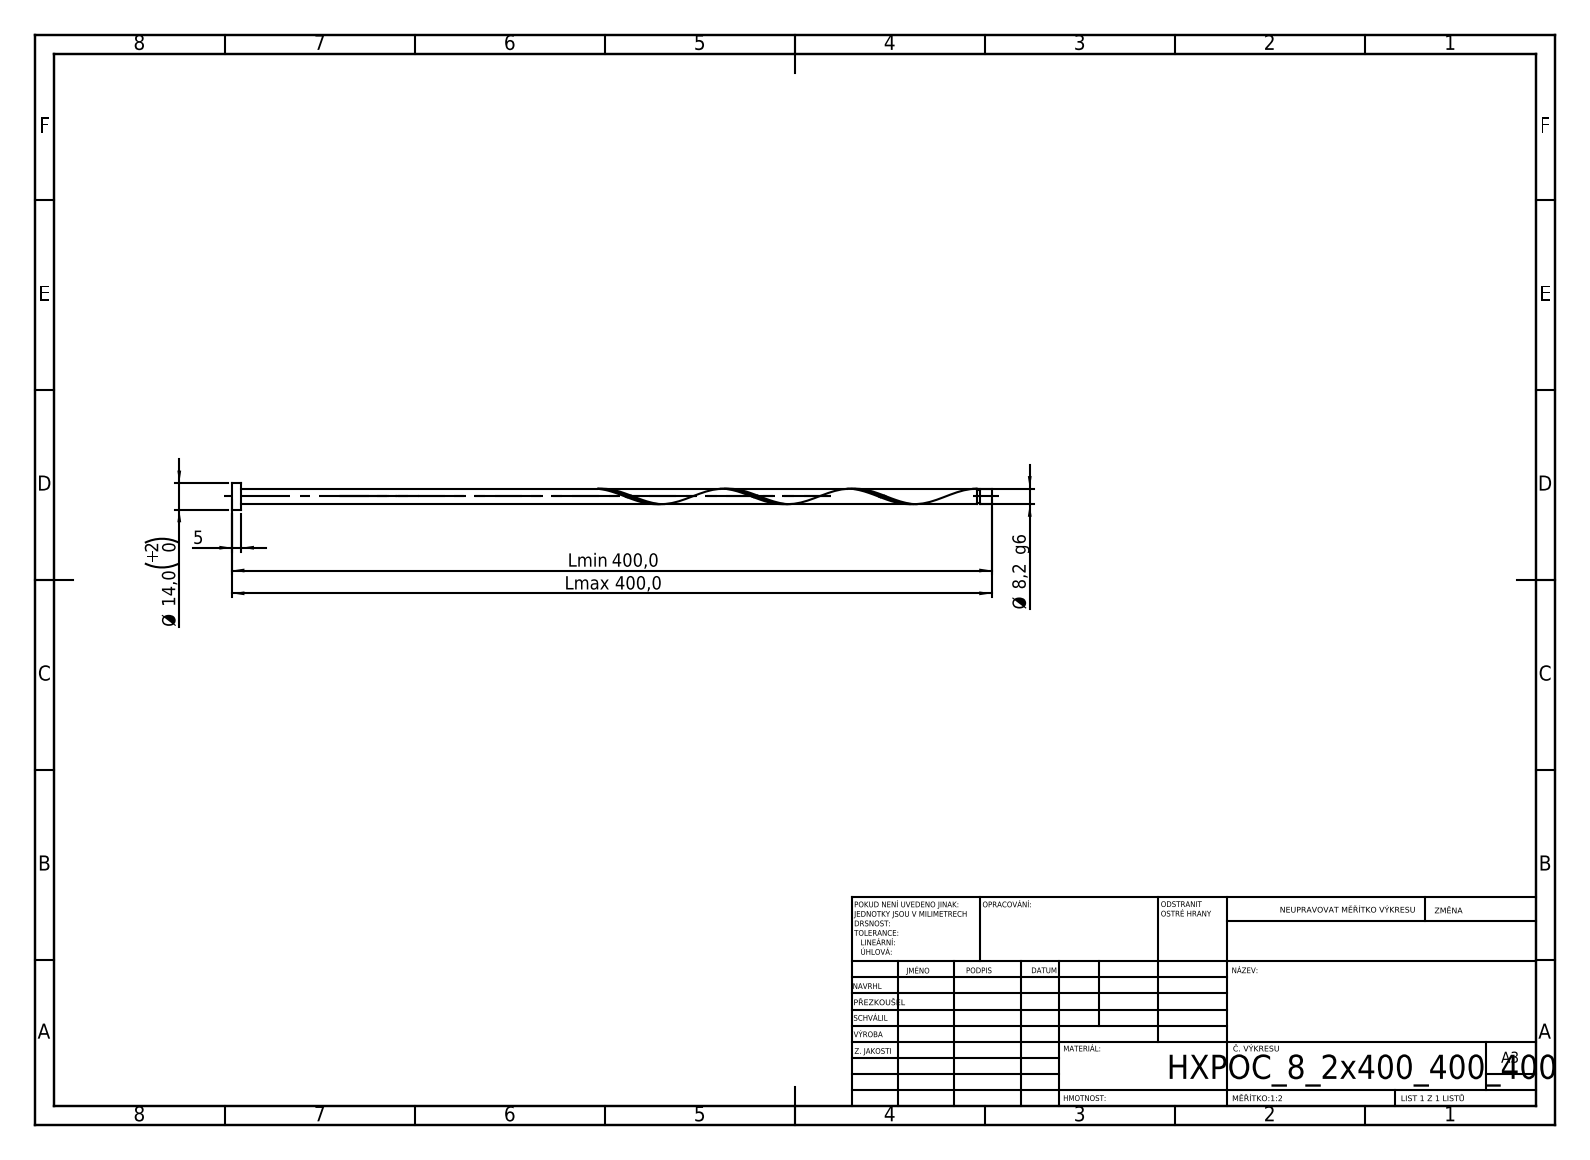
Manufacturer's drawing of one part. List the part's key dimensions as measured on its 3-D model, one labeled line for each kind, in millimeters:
STEP written by: SolidWorks 2019 (CONFIG_CONTROL_DESIGN)
Units: millimetres
Bodies: 1 solid, 21 faces (6 planar, 14 cylindrical, 1 other)
Overall size (bounding box): 400 × 14 × 14
Volume: 21 396 mm³ · Surface area: 10 903 mm²
Round bosses / shafts (diameter × count): ⌀14 ×1, ⌀8.2 ×1, ⌀6.56 ×1
Main face-to-face distances: 5, 400, 395, 394.04, 389.04, 5.96, 392.4, 387.4, 1.64, 7.6
